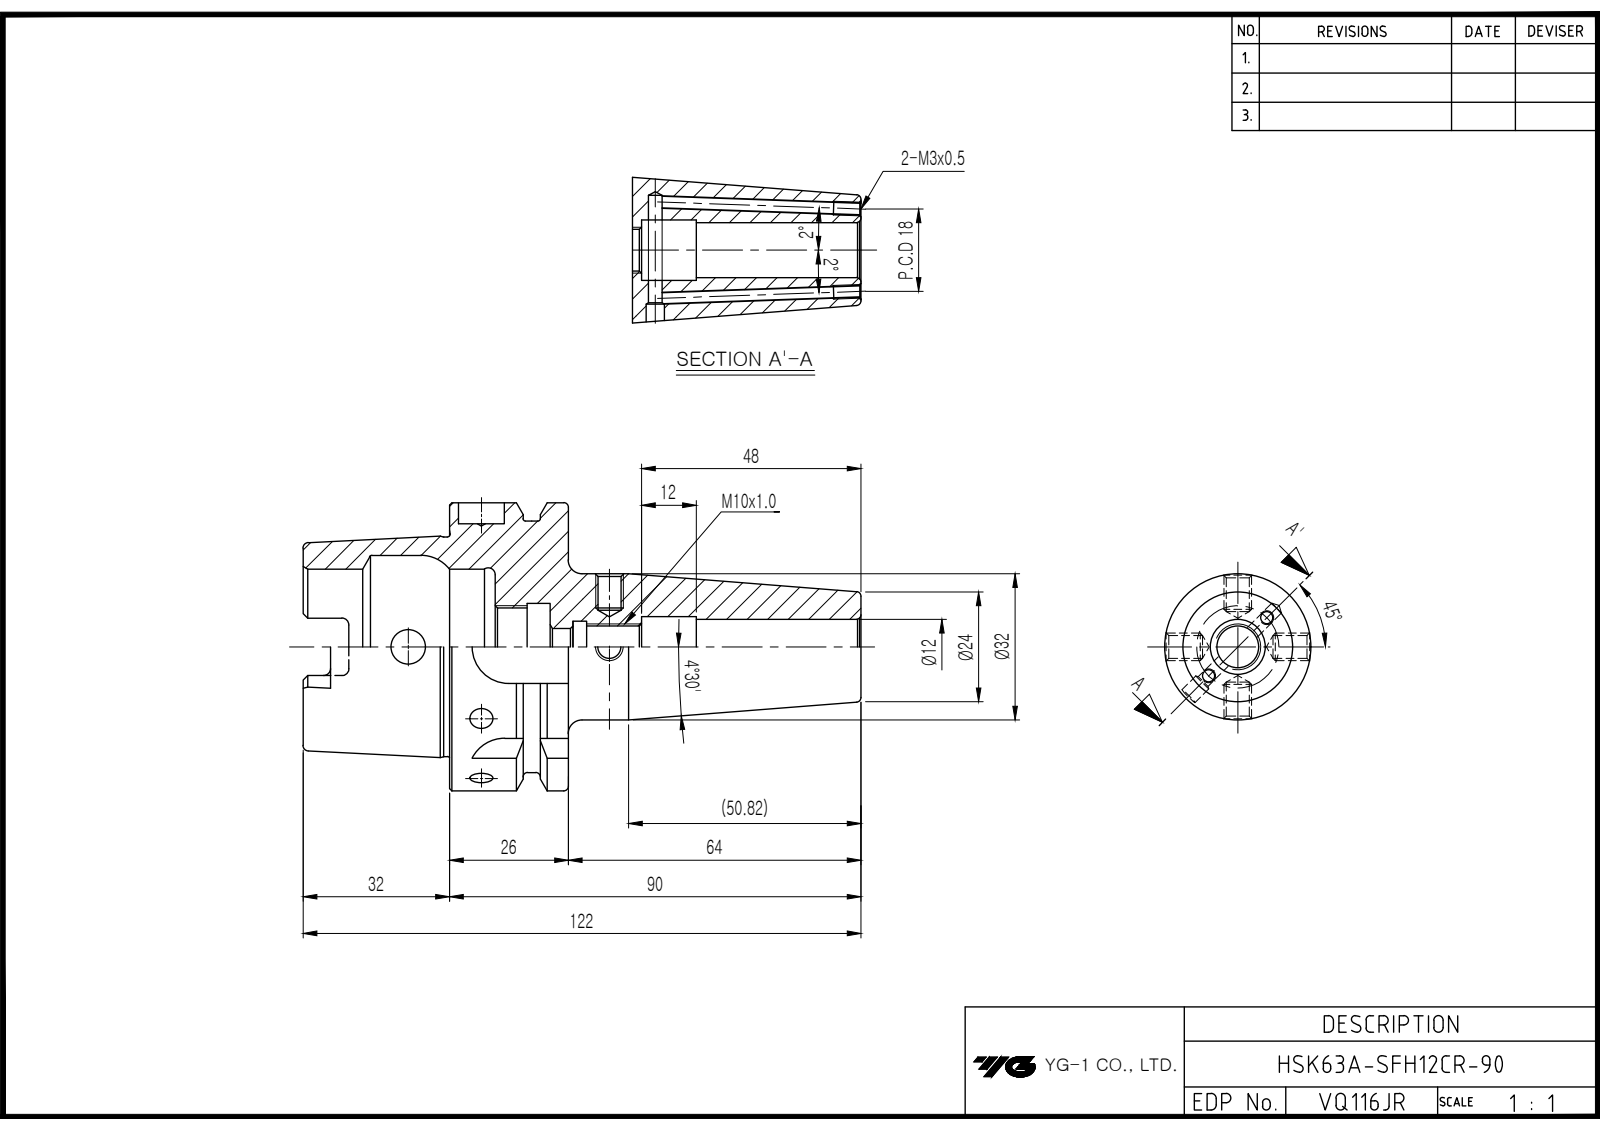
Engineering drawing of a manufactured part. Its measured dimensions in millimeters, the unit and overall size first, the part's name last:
Units: millimetres
Overall size (bounding box): 122 × 63 × 63
Round holes (diameter × count): ⌀2.46 ×2, ⌀7.5 ×1, ⌀8 ×1, ⌀8.92 ×1, ⌀10 ×1, ⌀11.6 ×1, ⌀12 ×1, ⌀13.2 ×1, ⌀16.92 ×1, ⌀19 ×1, ⌀34 ×1, ⌀40 ×1
Round bosses / shafts (diameter × count): ⌀63 ×1, ⌀55 ×1, ⌀48.04 ×1, ⌀32 ×1
Partial cylindrical surfaces — rounded edges, fillets, slot ends (radius × count): R1.5 ×6, R2.88 ×4, R8 ×4
Main face-to-face distances: 26, 10, 16, 32, 42, 58, 53, 12, 4, 22
Volume: 116 492 mm³ · Surface area: 30 727 mm²
Bodies: 1 solid, 123 faces (44 planar, 37 cylindrical, 42 other)
Part name (STEP PRODUCT): LO-HSK63A-SFH12CR-90
STEP written by: Autodesk Inventor 2022 (AUTOMOTIVE_DESIGN)
